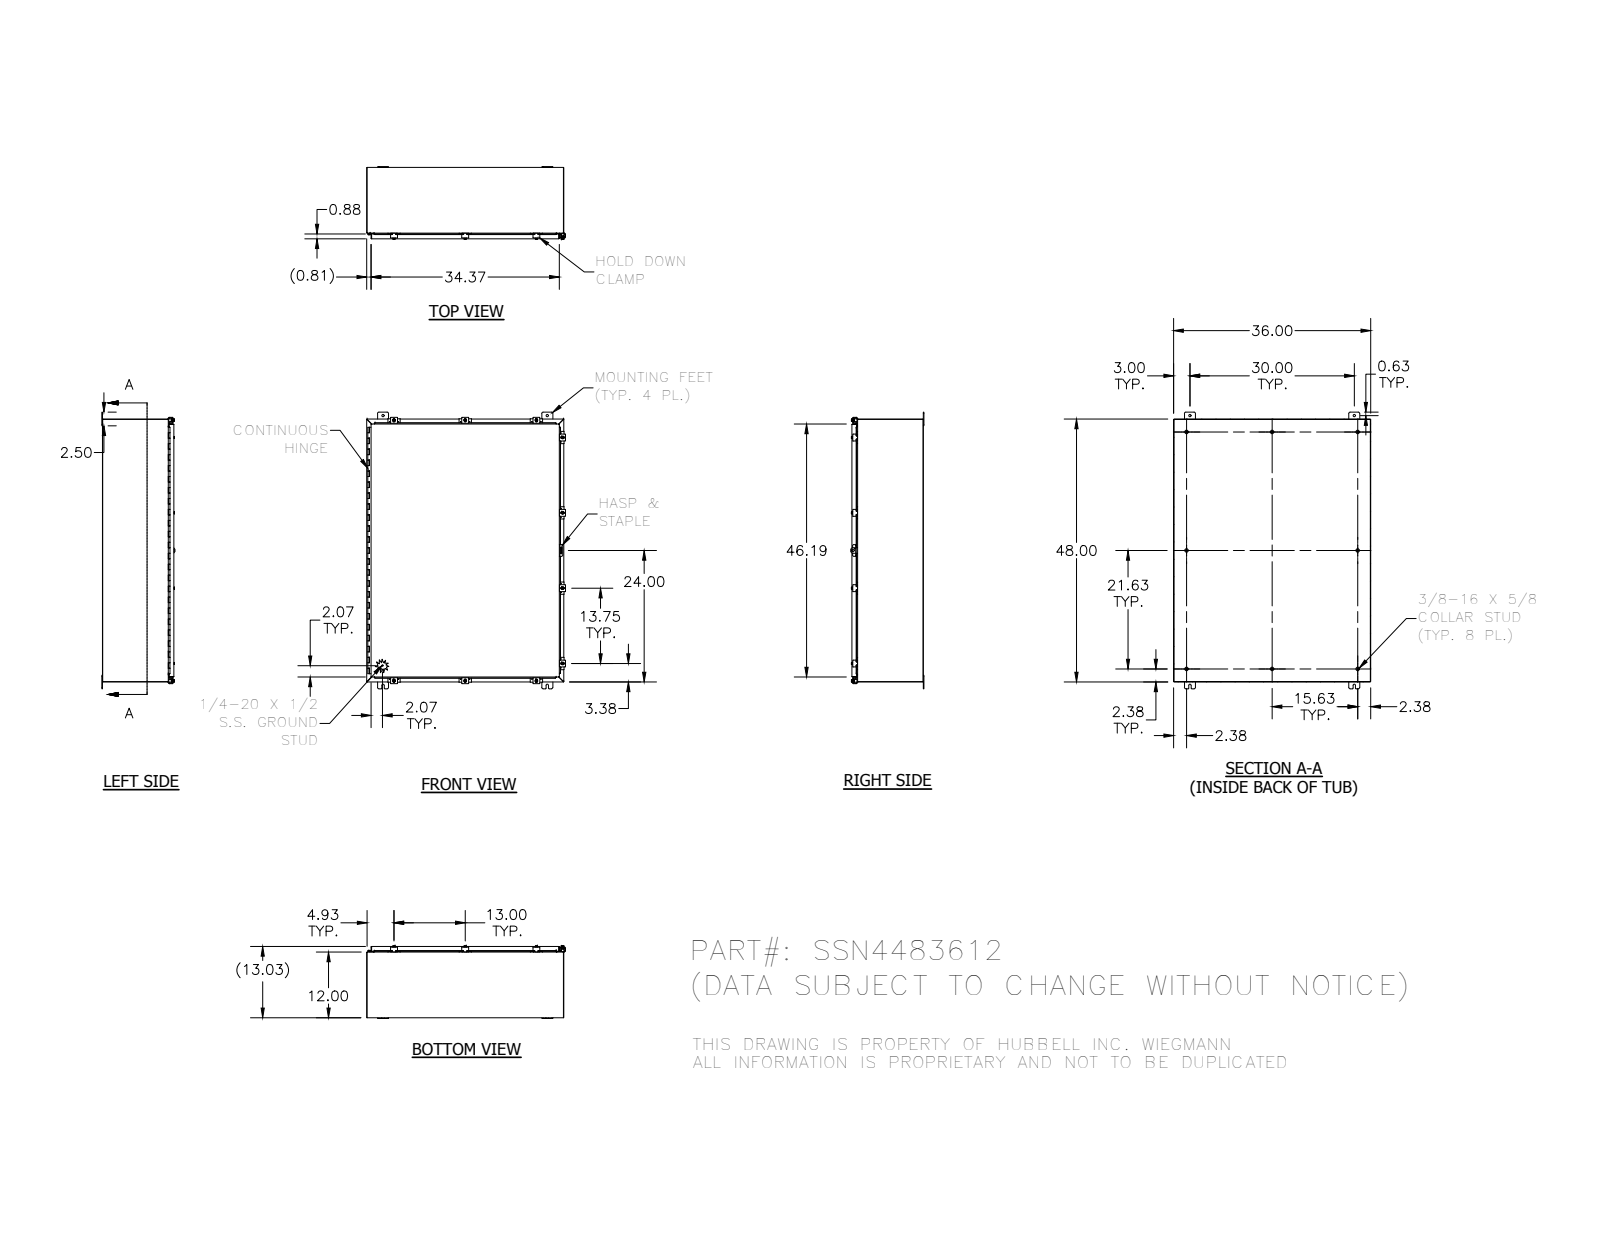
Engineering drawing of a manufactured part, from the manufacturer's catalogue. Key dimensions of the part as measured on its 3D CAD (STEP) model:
Part name (STEP PRODUCT): HFW30825-4; 30824; 32874-48L; HFW30825-3 (+8 more)
STEP written by: SolidWorks 2014 (AUTOMOTIVE_DESIGN)
Units: inches
Bodies: 73 solids, 2902 faces (1139 planar, 1258 cylindrical, 505 other)
Overall size (bounding box): 50.5 × 36.311 × 13.355
Volume: 463 in³ · Surface area: 12 292 in²
Round holes (diameter × count): ⌀0.11 ×23, ⌀0.211 ×10, ⌀0.281 ×10, ⌀0.3 ×10, ⌀0.438 ×4, ⌀0.125 ×1, ⌀0.156 ×1, ⌀0.5 ×1
Round bosses / shafts (diameter × count): ⌀0.25 ×12, ⌀0.52 ×10, ⌀0.5 ×10, ⌀0.35 ×10, ⌀0.625 ×8, ⌀0.33 ×8, ⌀0.337 ×1, ⌀0.12 ×1
Partial cylindrical surfaces — rounded edges, fillets, slot ends (radius × count): R0.03 ×117, R0.125 ×41, R0.25 ×37, R0.031 ×21, R0.105 ×21, R0.141 ×20, R0.062 ×18, R0.1 ×14
Main face-to-face distances: 0.074, 12.959, 12.885, 13.033, 35.926, 47.926, 35.852, 36, 47.852, 48
Hole centre spacings: 0.876, 13, 47.296, 12.192, 13.817, 48.727, 48.834, 49.265
